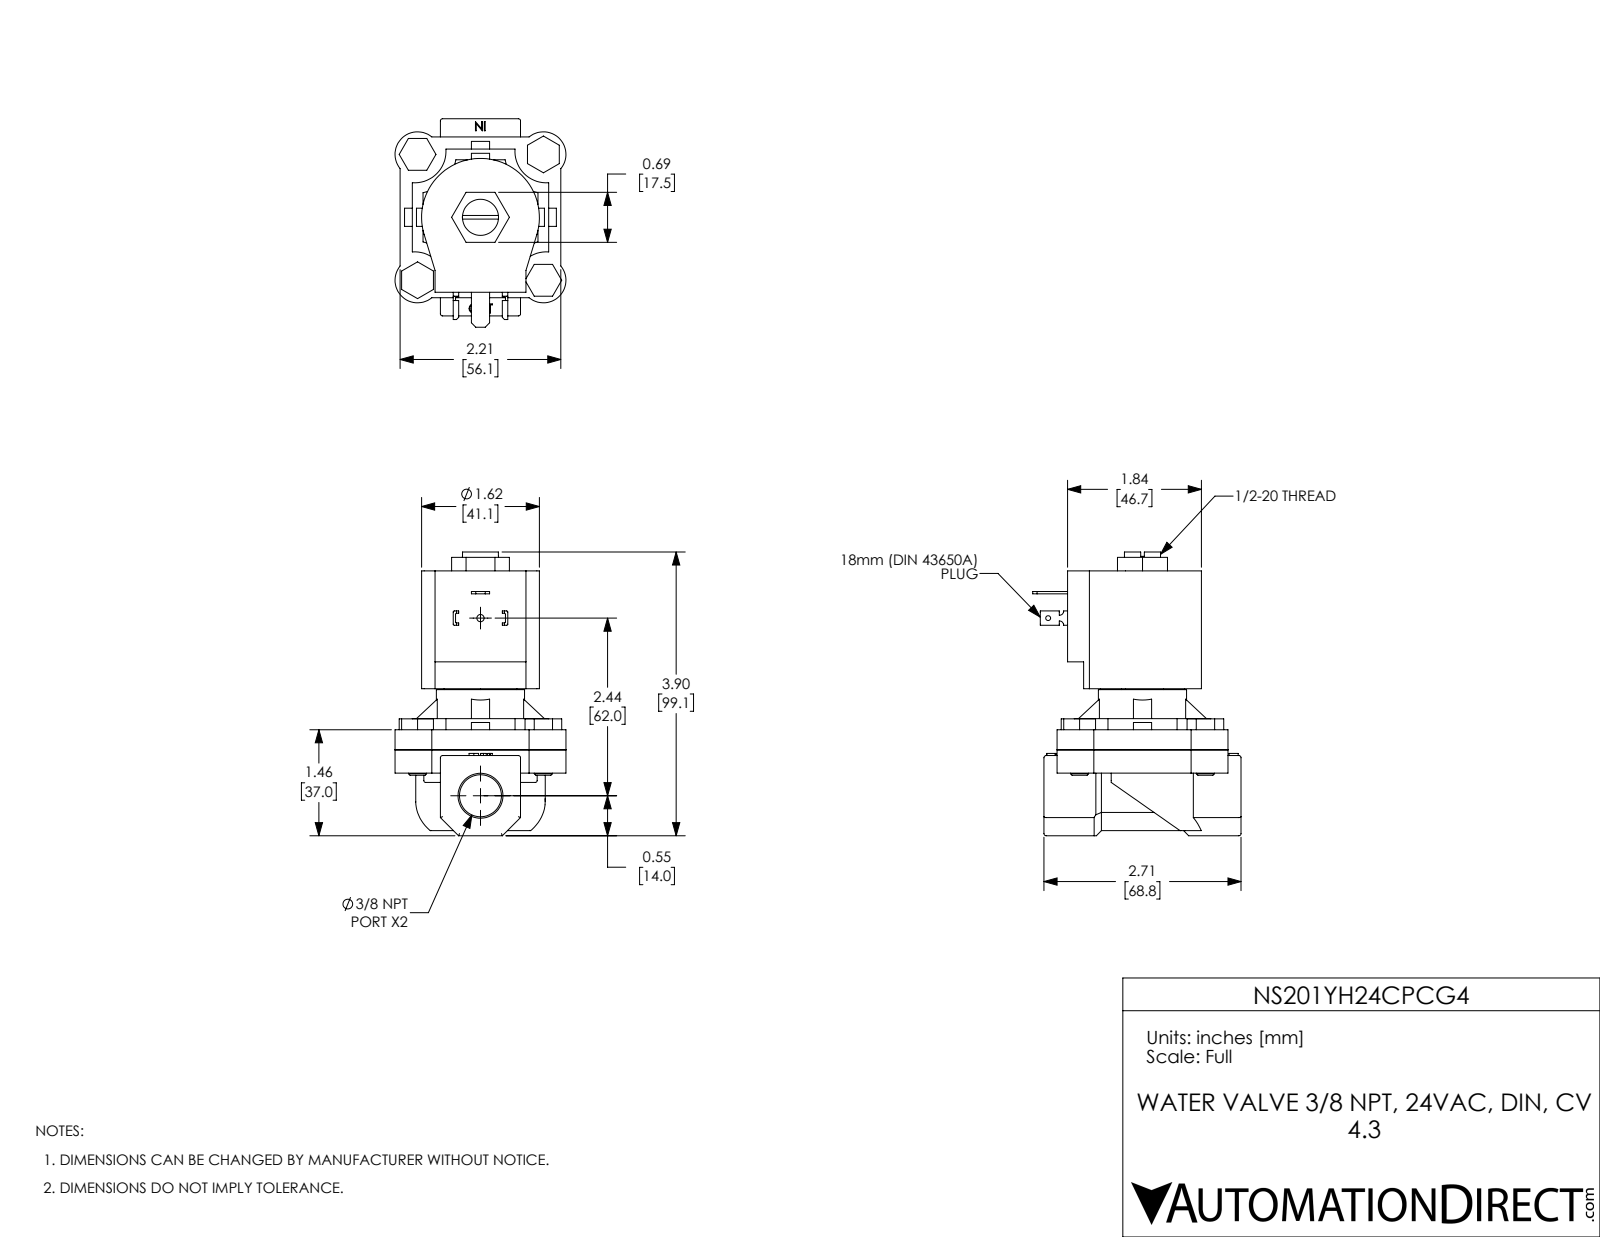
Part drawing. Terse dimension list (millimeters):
name: NS201YH24CPCG4
written by: SolidWorks 2024 (CONFIG_CONTROL_DESIGN)
unit: mm
bodies: 11 solids, 383 faces (237 planar, 113 cylindrical, 33 other)
size: 99.1 × 72.8 × 59.7
volume: 168 300 mm³; area: 42 940 mm²
holes: 4× ⌀6.4, 1× ⌀1.7, 1× ⌀2.5, 1× ⌀12.6, 1× ⌀13, 1× ⌀14.7, 1× ⌀29.3
bosses: 4× ⌀6.3, 1× ⌀30.8
rounds: 15× R0.8, 8× R0.4, 4× R7.9, 4× R11, 4× R14.7, 2× R1.5, 1× R20.6, 1× R22.6
face distances: 7, 62.5, 55.4, 8.1, 15.1, 70.6, 14.1, 42.1, 6.4, 28
hole spacings: 31.1, 43.9, 62.1, 62
